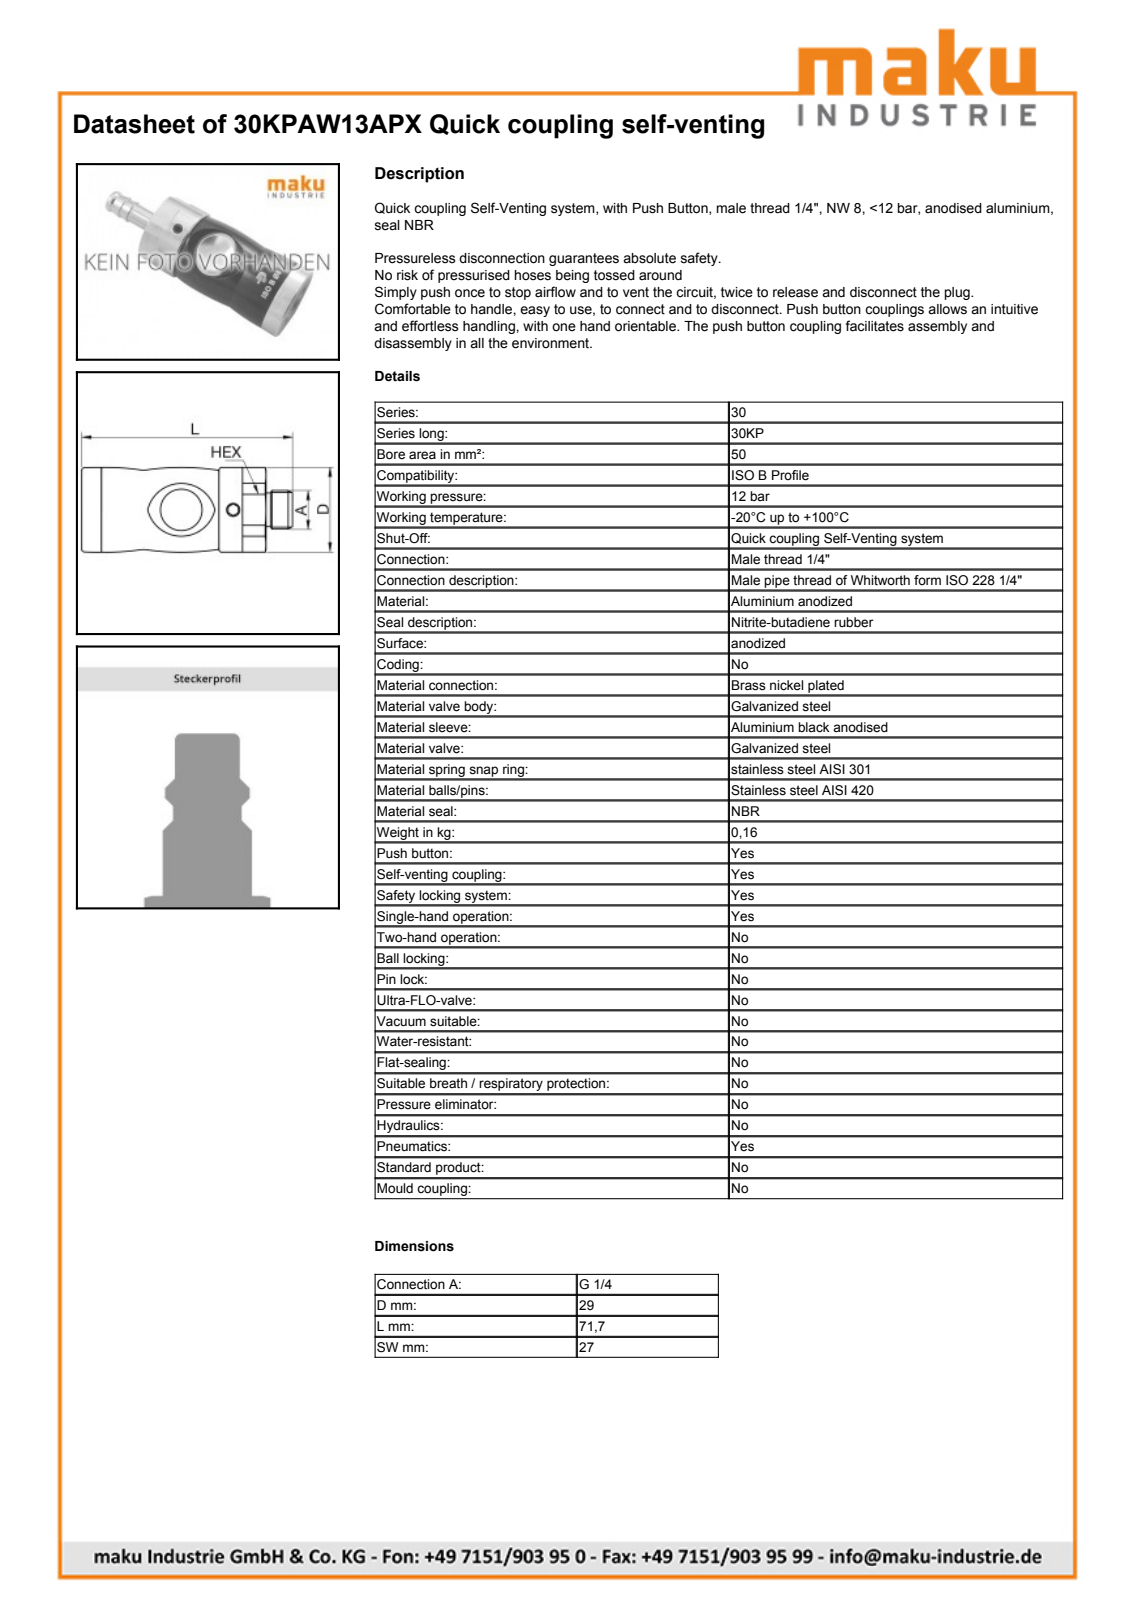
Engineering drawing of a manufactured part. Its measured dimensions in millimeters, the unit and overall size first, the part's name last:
Units: millimetres
Overall size (bounding box): 71.7 × 29.04 × 29.04
Round holes (diameter × count): ⌀3.5 ×1, ⌀8.5 ×1, ⌀9 ×1, ⌀11.2 ×1, ⌀12.2 ×1, ⌀14 ×1, ⌀15.3 ×1, ⌀16 ×1, ⌀17.5 ×1, ⌀18.1 ×1, ⌀20.61 ×1, ⌀20.7 ×1
Round bosses / shafts (diameter × count): ⌀29.01 ×1, ⌀26 ×1, ⌀24.5 ×1, ⌀24.21 ×1, ⌀24 ×1, ⌀20.5 ×1, ⌀18.2 ×1, ⌀18.18 ×1
Partial cylindrical surfaces — rounded edges, fillets, slot ends (radius × count): R2.5 ×4, R7.1 ×2
Main face-to-face distances: 62.7, 56, 16, 46.7, 6.7, 40, 9, 27, 62.1, 46.1
Hole centre spacings: 17.65
Volume: 45 323 mm³ · Surface area: 27 078 mm²
Bodies: 42 solids, 250 faces (74 planar, 75 cylindrical, 101 other)
Part name (STEP PRODUCT): 30KPAW13APX
STEP written by: Autodesk Inventor 2019 (CONFIG_CONTROL_DESIGN)
